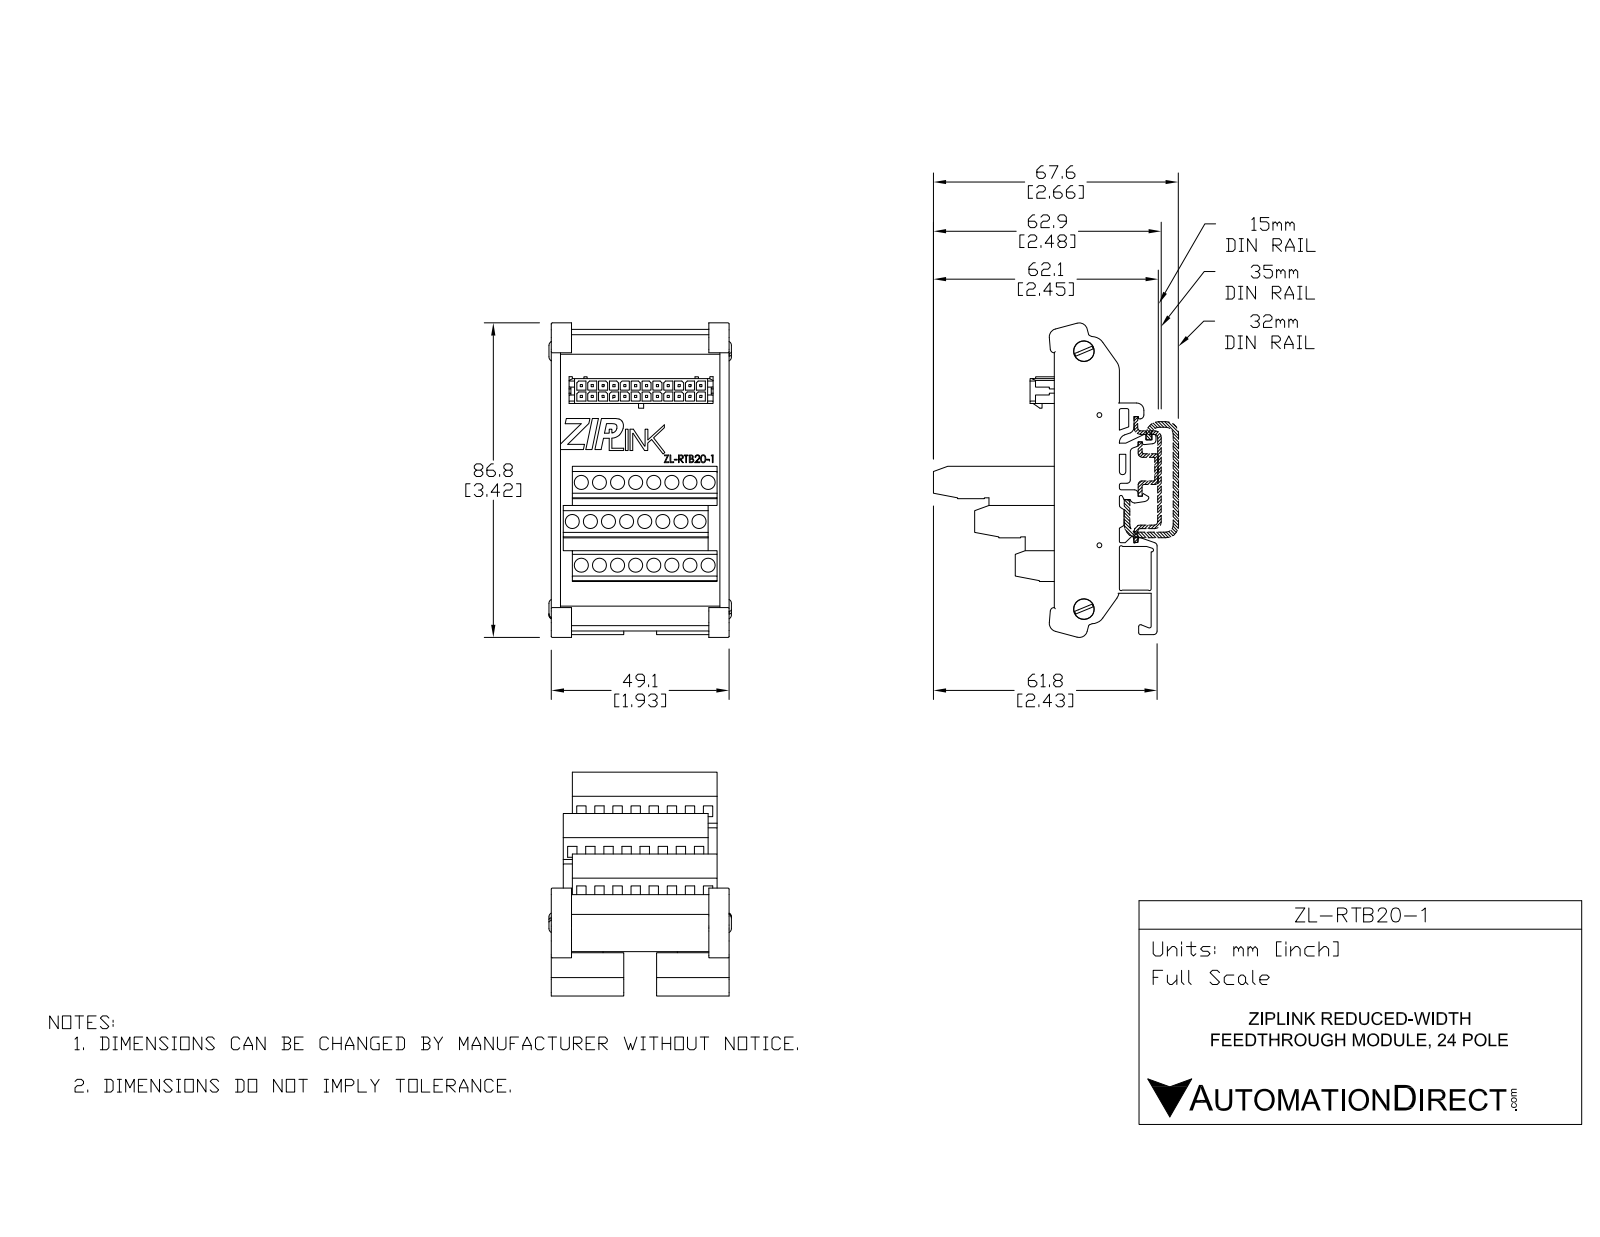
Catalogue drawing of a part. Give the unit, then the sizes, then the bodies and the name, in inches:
Units: inches
Overall size (bounding box): 3.419 × 2.432 × 1.969
Round holes (diameter × count): ⌀0.016 ×24, ⌀0.034 ×24, ⌀0.152 ×24, ⌀0.055 ×19, ⌀0.055 ×5, ⌀0.052 ×2, ⌀0.138 ×2, ⌀0.24 ×2
Round bosses / shafts (diameter × count): ⌀0.063 ×24, ⌀0.217 ×2, ⌀0.157 ×2, ⌀0.118 ×2
Partial cylindrical surfaces — rounded edges, fillets, slot ends (radius × count): R0.02 ×50, R0.02 ×50, R0.01 ×24, R0.012 ×10, R0.035 ×5, R0.039 ×5, R0.05 ×5, R0.079 ×4
Main face-to-face distances: 0.059, 0.213, 0.061, 0.117, 0.178, 0.272, 0.389, 0.45, 0.07, 0.176
Hole centre spacings: 0.197, 0.394, 0.608, 0.412, 0.591, 0.669, 1.019, 0.497
Volume: 3.95 in³ · Surface area: 94.13 in²
Bodies: 10 solids, 2052 faces (1284 planar, 680 cylindrical, 88 other)
Part name (STEP PRODUCT): ZL-RTB20-1
STEP written by: SolidWorks 2016 (AUTOMOTIVE_DESIGN)
